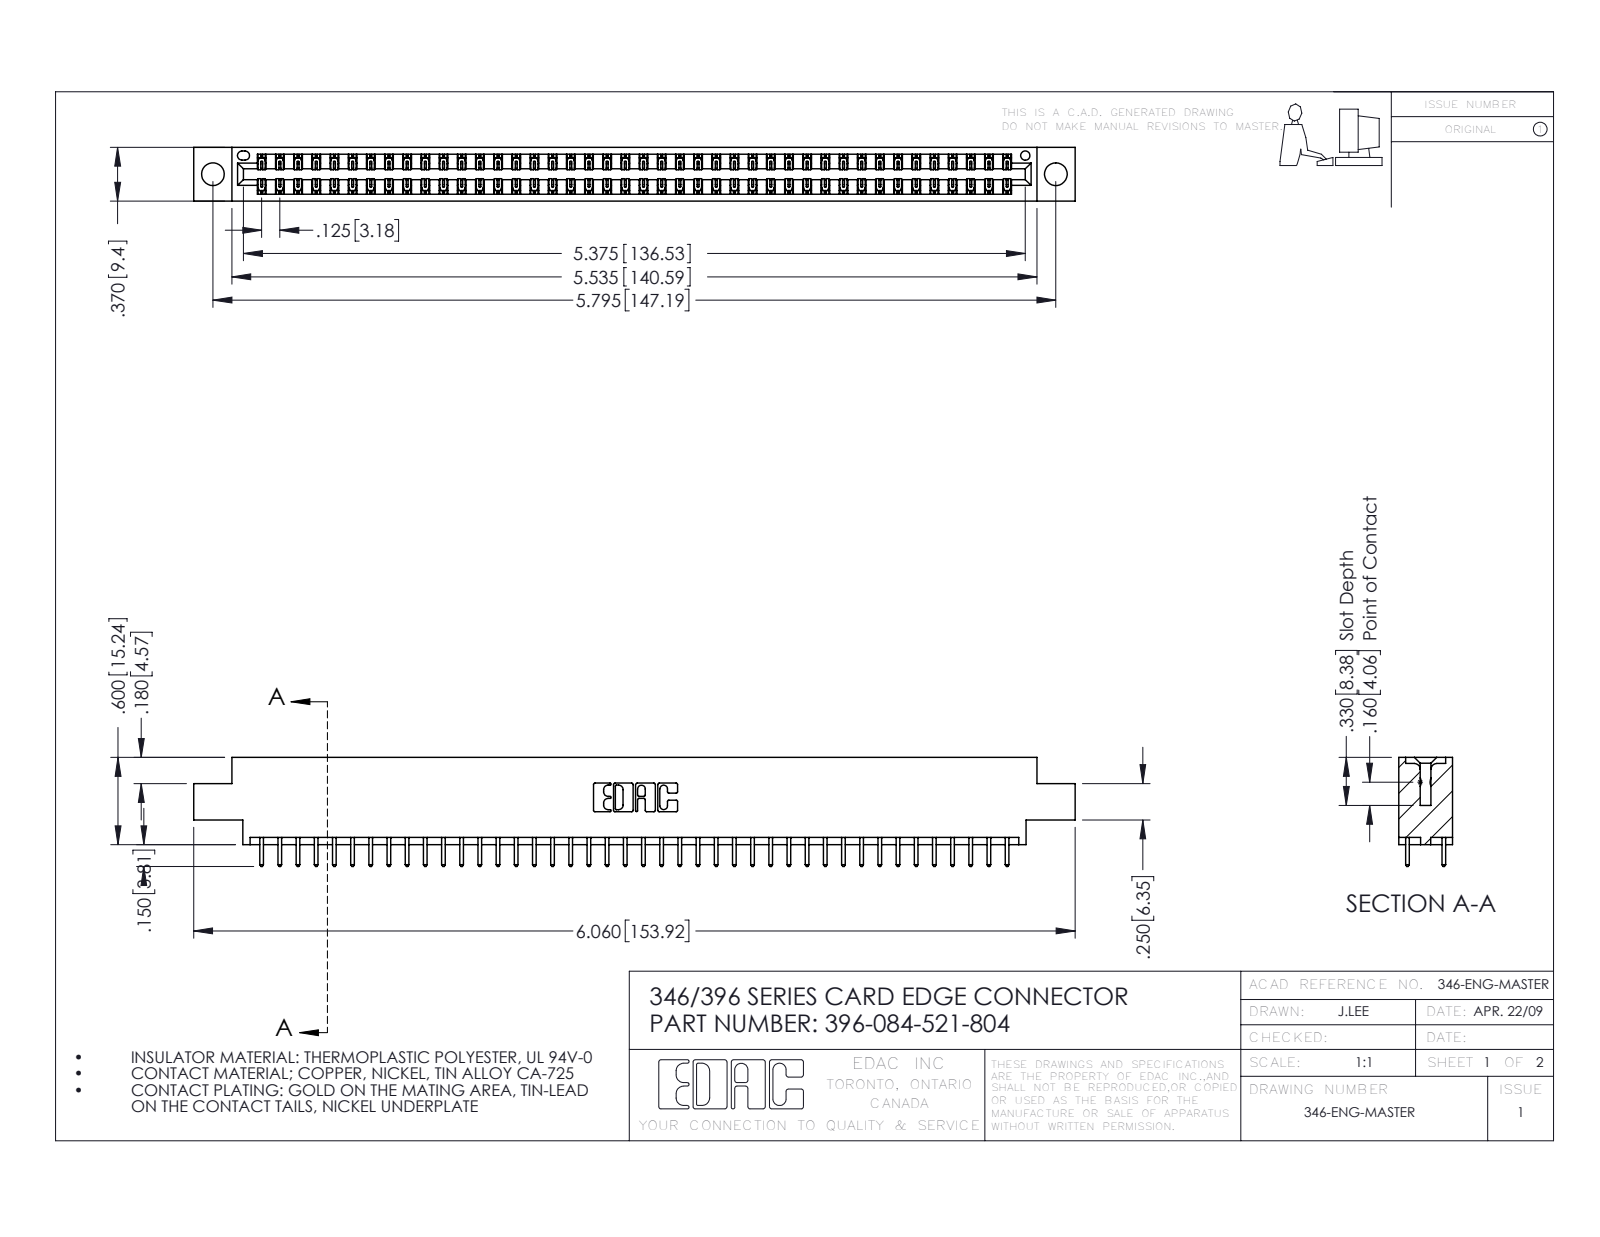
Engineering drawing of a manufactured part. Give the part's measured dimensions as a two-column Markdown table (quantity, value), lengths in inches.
| quantity | value |
| --- | --- |
| part name | 396-084-521-804; 346 Part_0.170 Offset - 0.156 Dia-TH; 345-292-001_345-293-121 |
| STEP written by | SolidWorks 2016 (CONFIG_CONTROL_DESIGN) |
| units | inches |
| bodies | 85 solids, 4494 faces (3020 planar, 1474 cylindrical, 0 other) |
| overall size | 6.06 × 0.75 × 0.37 |
| volume | 0.899 in³ |
| surface area | 31.02 in² |
| round holes (diameter × count) | 0.156 × 2, 0.064 × 1 |
| partial cylindrical surfaces (radius × count) | 0.006 × 126, 0.01 × 84, 0.01 × 22, 0.007 × 6, 0.031 × 6, 0.026 × 3, 0.014 × 2, 0.022 × 2 |
| main face-to-face distances | 0.048, 0.322, 0.37, 0.25, 0.072, 0.298, 0.025, 0.275, 0.148, 0.222 |
| hole center spacings | 0.246, 5.586, 5.795 |
